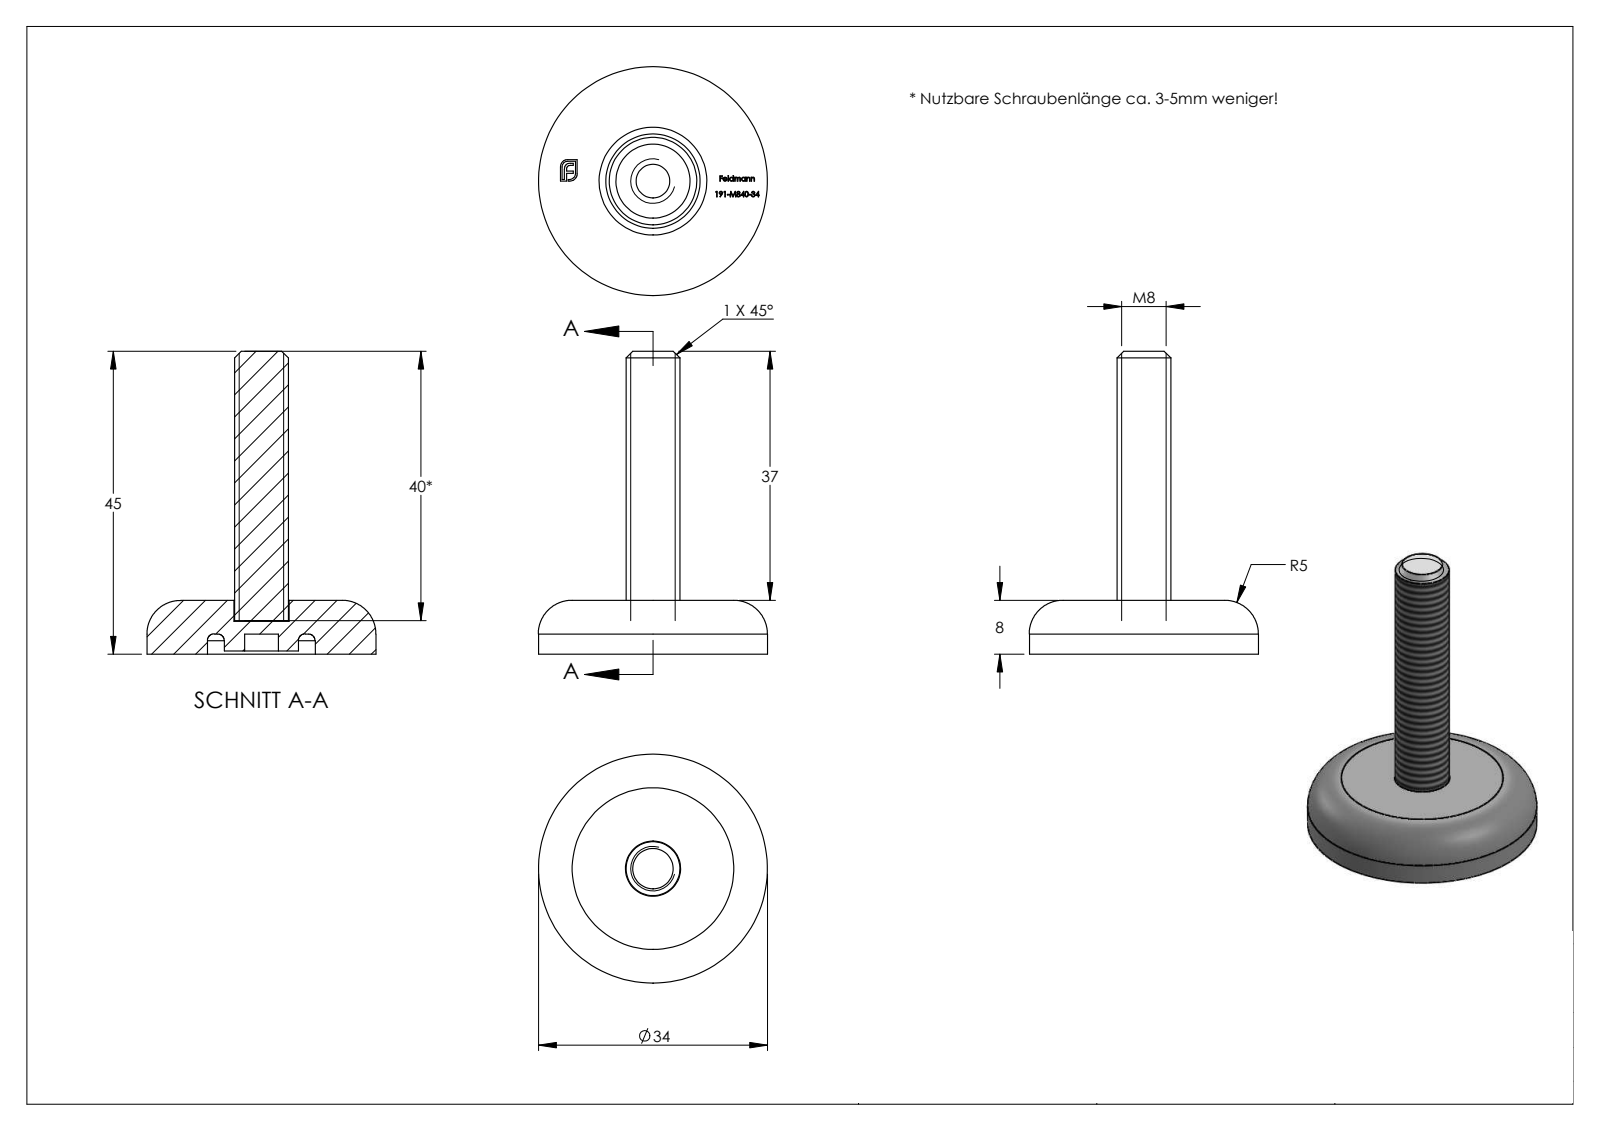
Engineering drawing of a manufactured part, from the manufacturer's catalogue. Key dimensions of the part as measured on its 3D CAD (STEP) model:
Part name (STEP PRODUCT): 191-M840-34
STEP written by: SolidWorks 2018 (CONFIG_CONTROL_DESIGN)
Units: millimetres
Bodies: 2 solids, 313 faces (176 planar, 12 cylindrical, 125 other)
Overall size (bounding box): 45 × 34 × 34
Volume: 8 166 mm³ · Surface area: 3 849 mm²
Round holes (diameter × count): ⌀5 ×1, ⌀8.2 ×1, ⌀16 ×1
Round bosses / shafts (diameter × count): ⌀34 ×1, ⌀11 ×1, ⌀8 ×1
Main face-to-face distances: 8, 5, 3, 0.5, 7.5, 4.9, 4.4, 3.1, 4.5, 1.9
